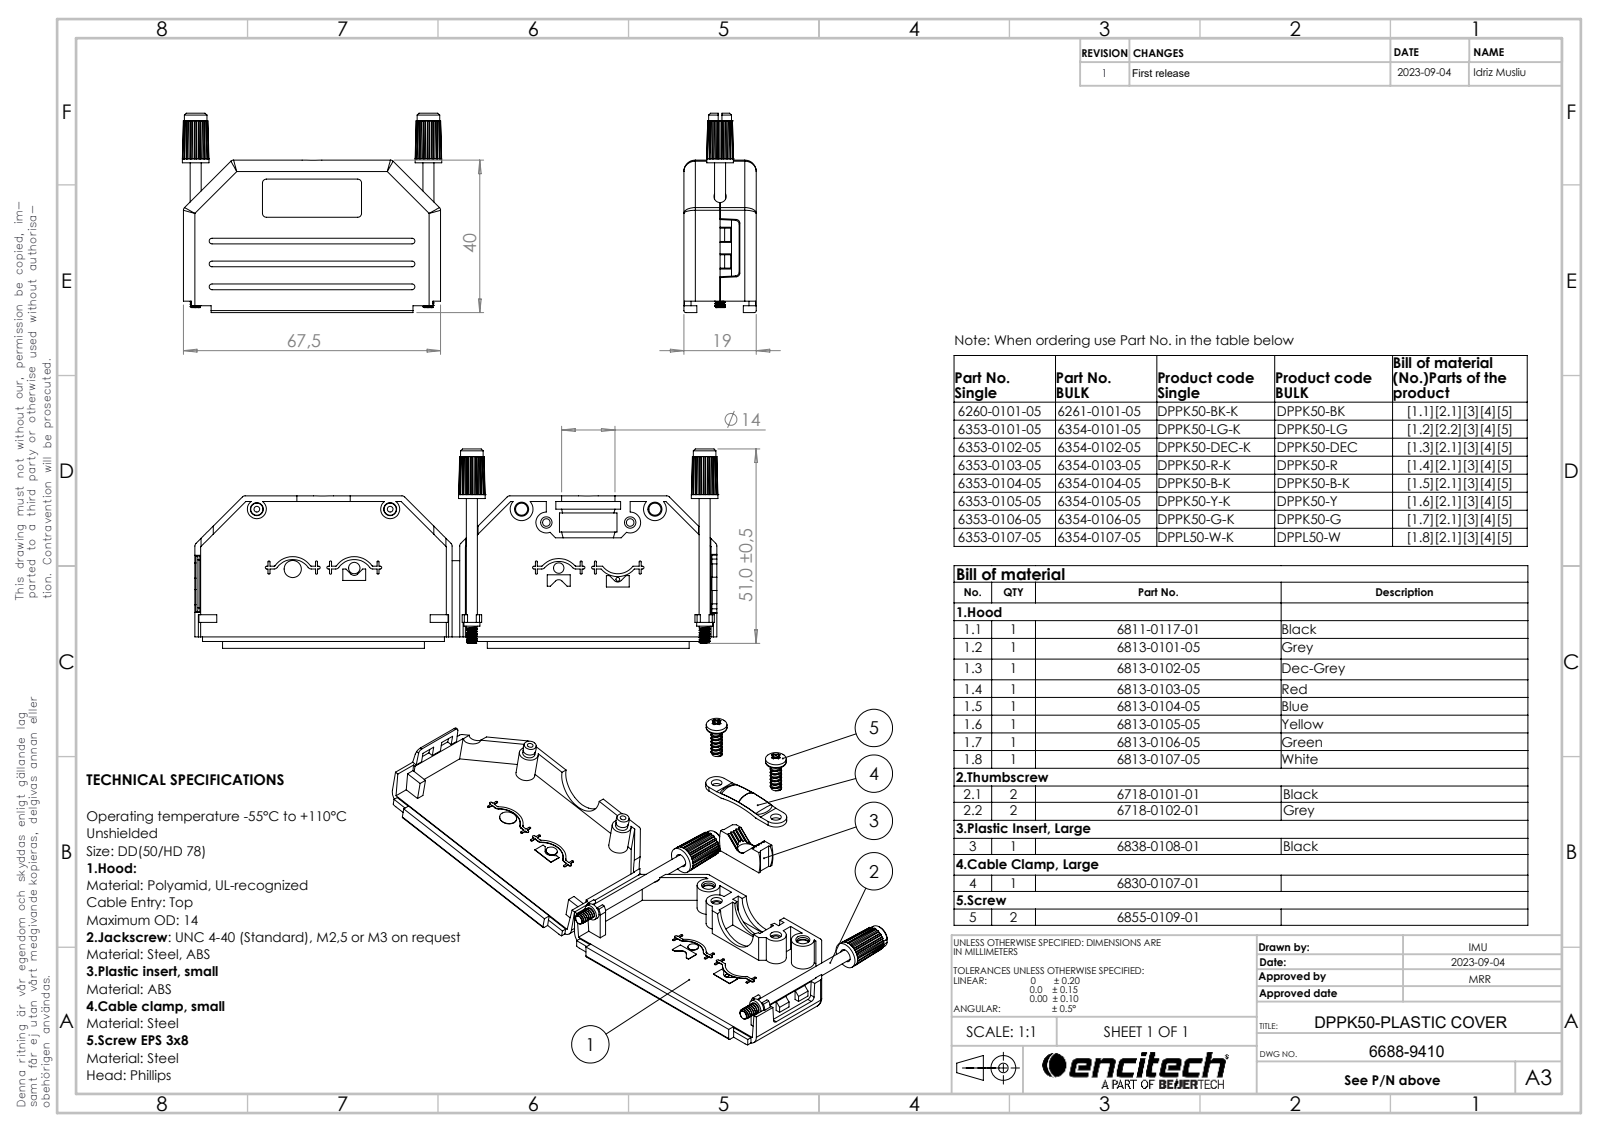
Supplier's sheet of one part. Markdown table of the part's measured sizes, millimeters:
| quantity | value |
| --- | --- |
| part name | 6718-0101-01; 6260-0101-05; 6811-0117-01 Part 1; 6811-0117-01 Part 2 (+3 more) |
| STEP written by | SolidWorks 2021 (AUTOMOTIVE_DESIGN) |
| units | millimeters |
| bodies | 10 solids, 881 faces (563 planar, 221 cylindrical, 97 other) |
| overall size | 68.1 × 52.3 × 19 |
| volume | 16 277 mm³ |
| surface area | 18 898 mm² |
| round holes (diameter × count) | 3.2 × 4, 1.5 × 2, 2 × 2, 2.8 × 2, 3 × 2, 3.7 × 2, 4.6 × 1, 14 × 1 |
| round bosses / shafts (diameter × count) | 7 × 2, 6 × 2, 5.45 × 2, 5 × 2, 4.2 × 2, 2.9 × 2, 4.5 × 1, 3 × 1 |
| partial cylindrical surfaces (radius × count) | 0.25 × 22, 1 × 22, 3 × 12, 0.38 × 8, 0.75 × 6, 0.47 × 4, 5 × 4, 5.75 × 4 |
| main face-to-face distances | 16.8, 2.2, 14.6, 19, 1.5, 9.5, 7.3, 16.7, 1.9, 9.4 |
| hole center spacings | 7.38, 28.71, 30.55, 10.99, 11.01, 17.84, 17.86, 22 |
